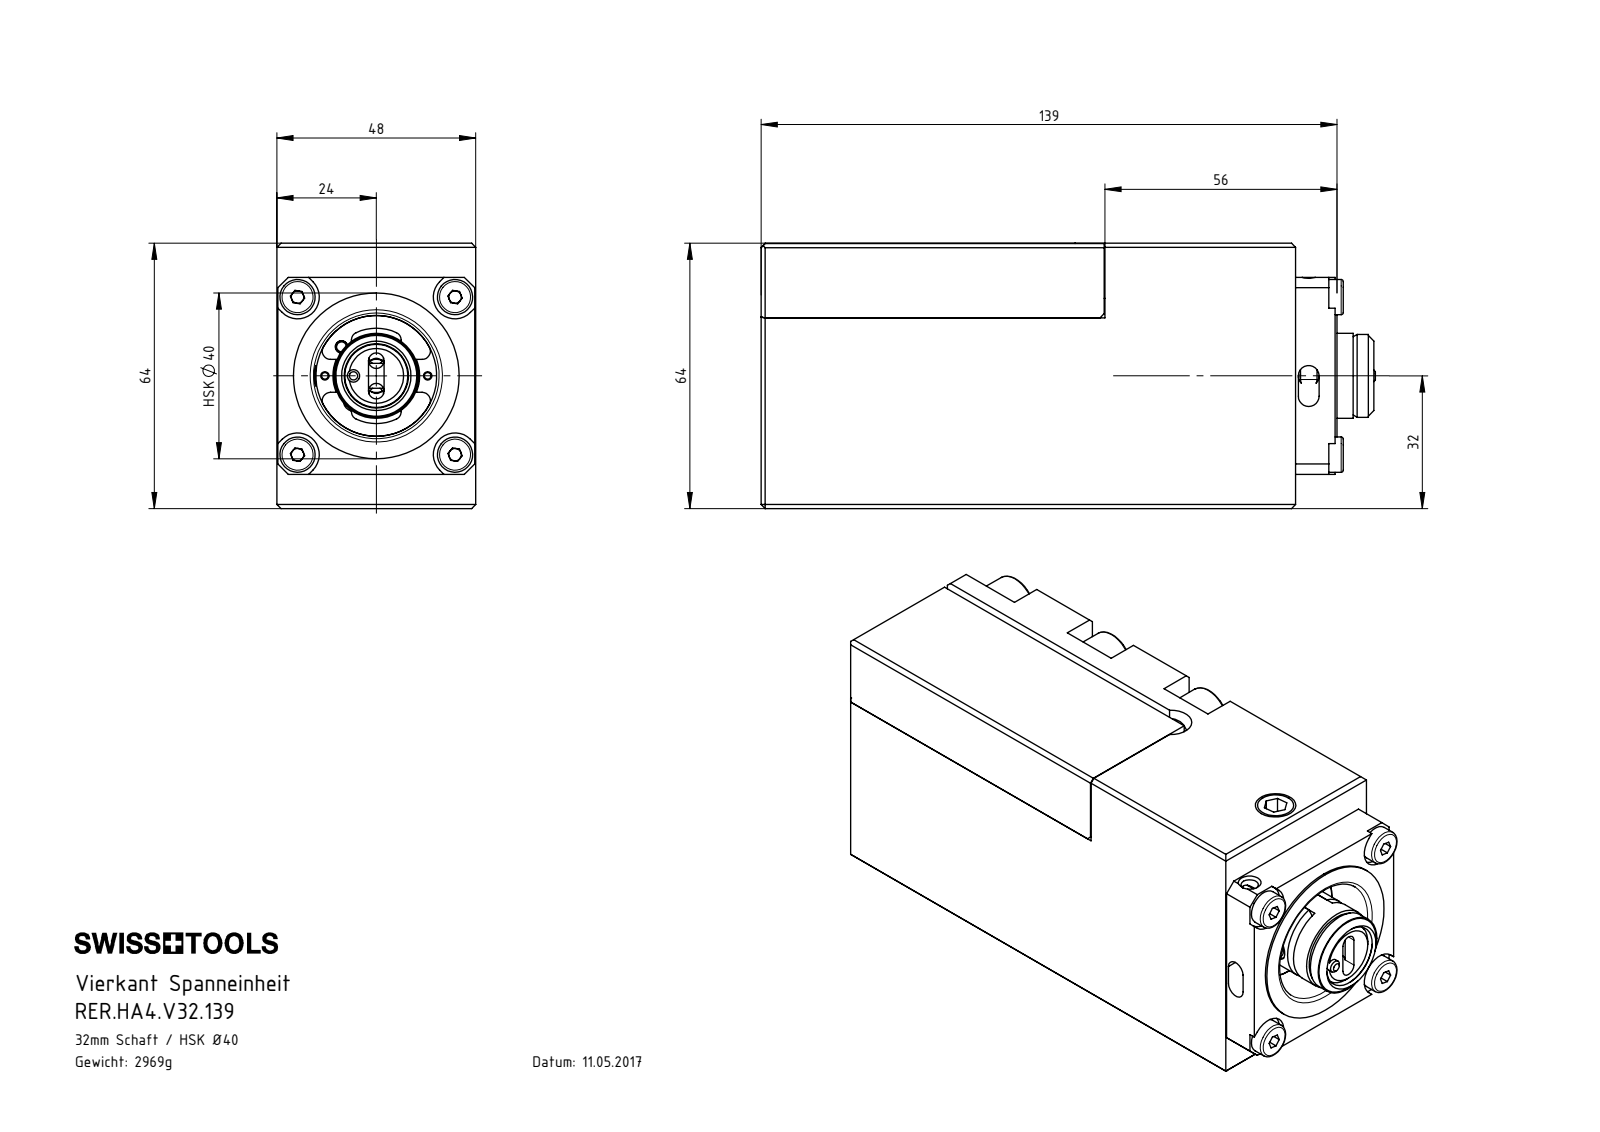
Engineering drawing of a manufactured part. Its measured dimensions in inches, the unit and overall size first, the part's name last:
Units: inches
Overall size (bounding box): 5.837 × 2.52 × 1.89
Round holes (diameter × count): ⌀0.165 ×5, ⌀0.217 ×4, ⌀0.268 ×3, ⌀0.354 ×3, ⌀0.063 ×2, ⌀0.118 ×2, ⌀0.13 ×2, ⌀0.138 ×2, ⌀0.148 ×2, ⌀0.094 ×1, ⌀0.157 ×1, ⌀0.197 ×1
Round bosses / shafts (diameter × count): ⌀0.197 ×5, ⌀0.335 ×4, ⌀0.512 ×3, ⌀0.315 ×3, ⌀1.575 ×1, ⌀1.559 ×1, ⌀1.555 ×1, ⌀1.488 ×1
Partial cylindrical surfaces — rounded edges, fillets, slot ends (radius × count): R0.039 ×8, R0.077 ×4, R0.079 ×4, R0.207 ×4, R0.295 ×3, R0.108 ×2, R0.02 ×1, R0.059 ×1
Main face-to-face distances: 1.89, 2.52, 2.516, 5.079, 3.425, 1.654, 0.079, 0.63, 0.197, 2.028
Hole centre spacings: 1.299, 0.509, 0.792, 0.961, 1.058, 1.165, 1.445, 1.496
Volume: 24.3 in³ · Surface area: 135.3 in²
Bodies: 24 solids, 705 faces (290 planar, 205 cylindrical, 210 other)
Part name (STEP PRODUCT): Dichtung; DIN 3771 - 12x1.5; DIN 3771 - 36x2; RER.HA4.V32.139 (+8 more)
STEP written by: SolidWorks 2022 (AUTOMOTIVE_DESIGN)
